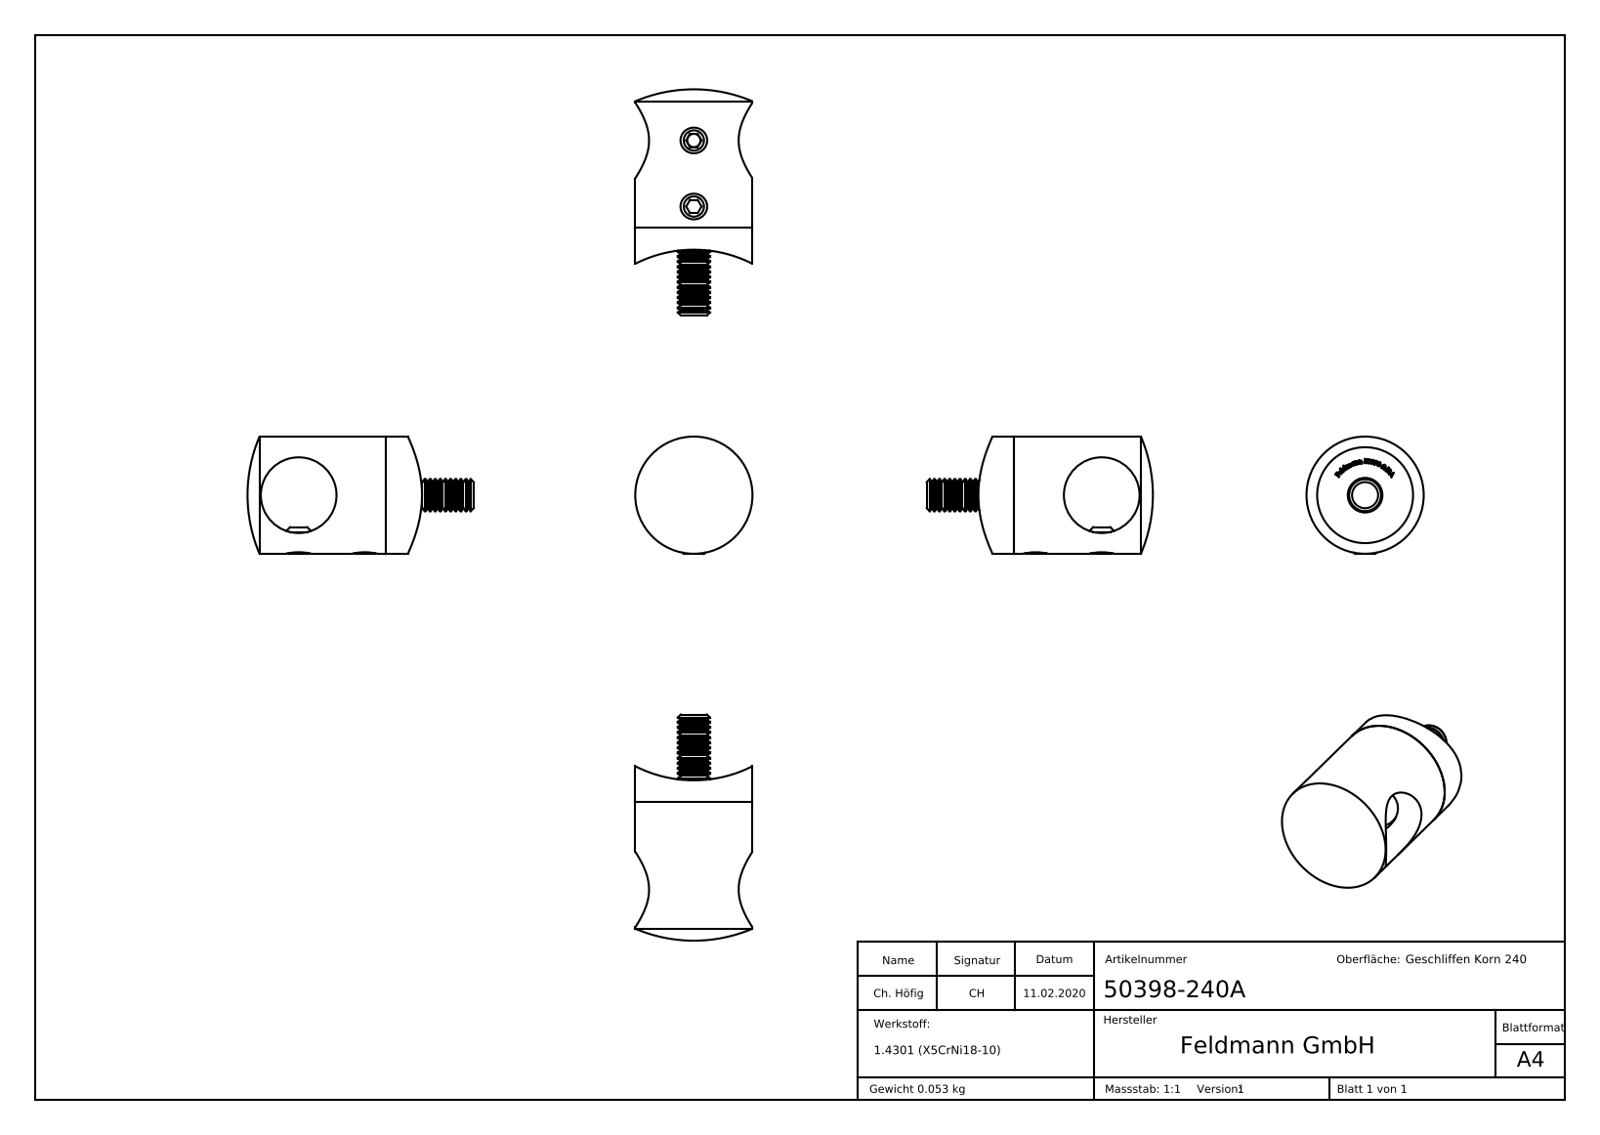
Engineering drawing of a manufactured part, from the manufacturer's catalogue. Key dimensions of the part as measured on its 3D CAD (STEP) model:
Part name (STEP PRODUCT): socket countersunk head screw_din_DIN 7991 - M6 x 25 --- 25S; DIN913_DIN 913 M5x5; Querstabhalter Teil2 Konfig_50XXX-240A Teil2 48,3; DIN913 (+7 more)
STEP written by: SolidWorks 2015 (CONFIG_CONTROL_DESIGN)
Units: millimetres
Bodies: 5 solids, 383 faces (169 planar, 36 cylindrical, 178 other)
Overall size (bounding box): 70 × 42.45 × 22
Volume: 7 423 mm³ · Surface area: 6 028 mm²
Round holes (diameter × count): ⌀4.2 ×2, ⌀6.5 ×1, ⌀12 ×1, ⌀14.2 ×1, ⌀18 ×1
Round bosses / shafts (diameter × count): ⌀5 ×2, ⌀22 ×1, ⌀11.9 ×1, ⌀11.57 ×1, ⌀6 ×1
Partial cylindrical surfaces — rounded edges, fillets, slot ends (radius × count): R24.15 ×1
Main face-to-face distances: 2.1, 10.65, 8.55, 2.5, 9.6, 7.5, 1.05, 14.35, 16.45, 23.95
Hole centre spacings: 12.4
